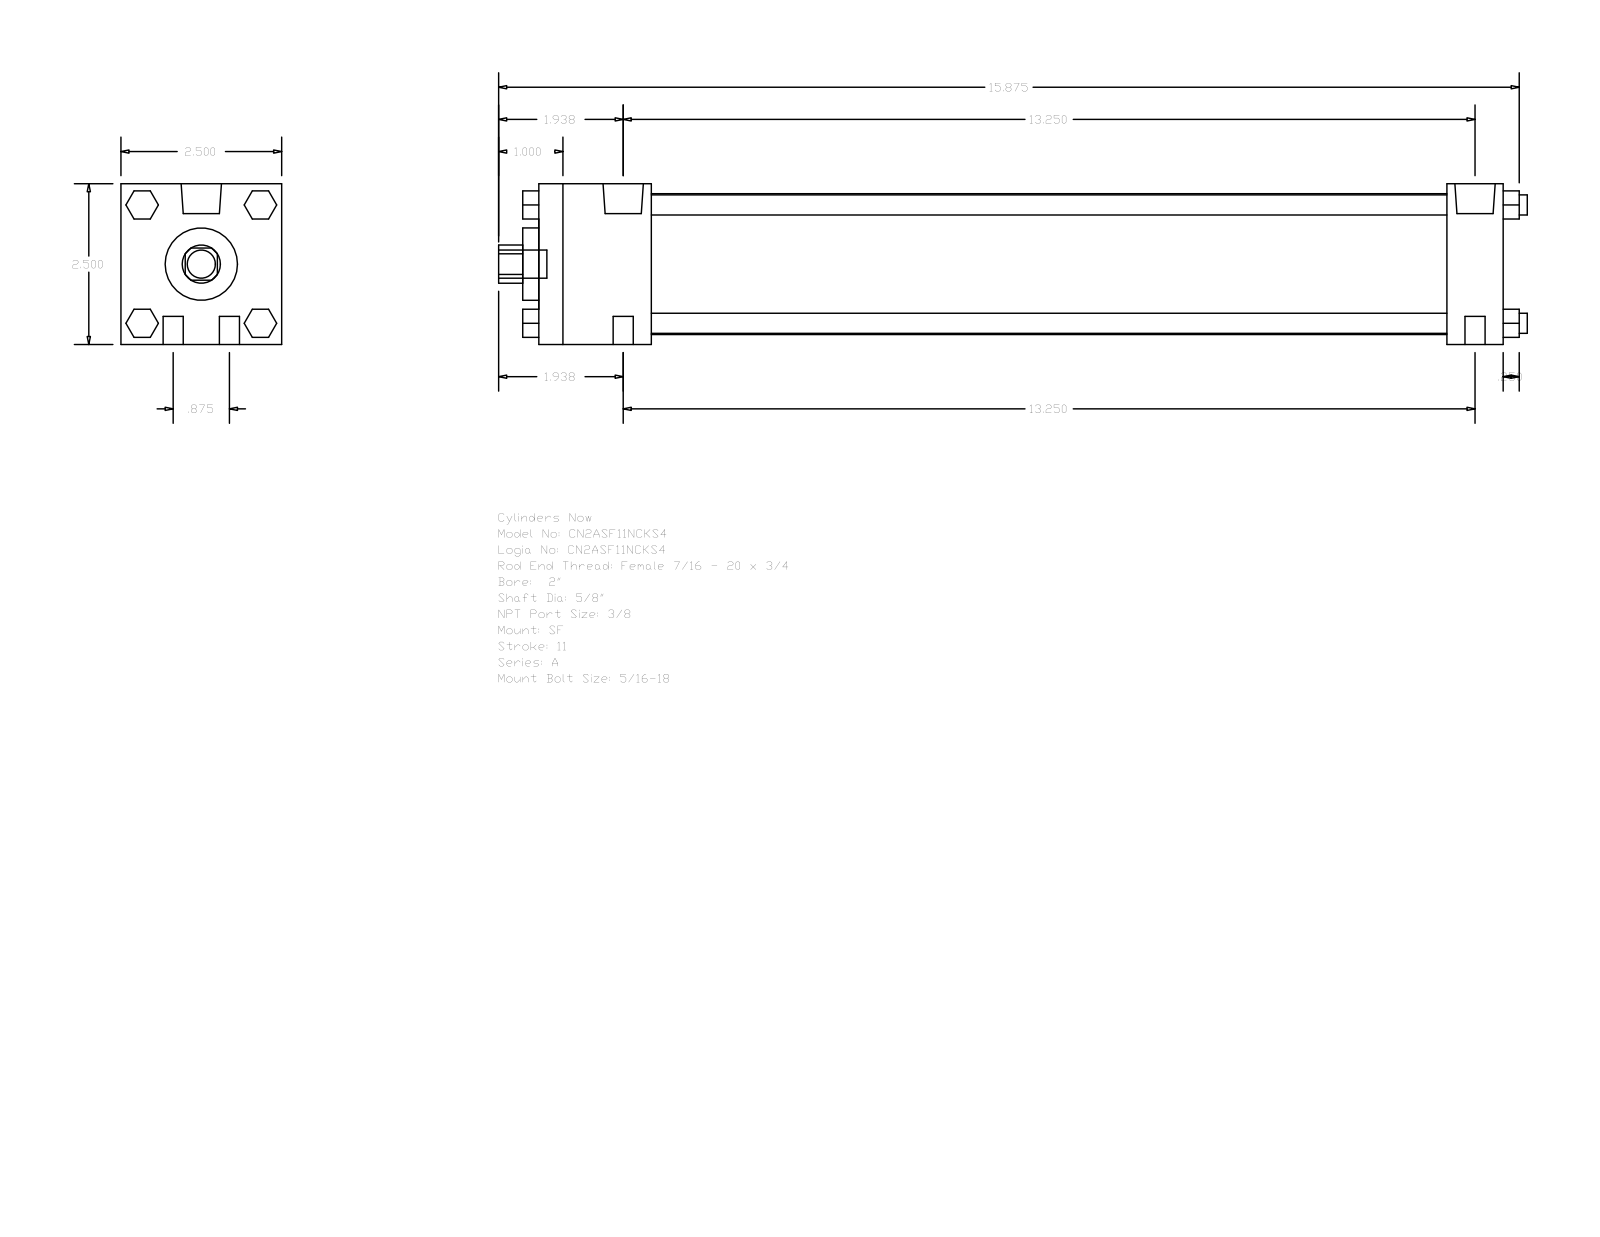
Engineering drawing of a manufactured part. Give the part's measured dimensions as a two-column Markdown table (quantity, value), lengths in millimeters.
| quantity | value |
| --- | --- |
| part name | A_SF__0200_0.625 |
| STEP written by | GSSL Pune (CONFIG_CONTROL_DESIGN) |
| units | millimeters |
| bodies | 0 solids, 124 faces (94 planar, 30 cylindrical, 0 other) |
| overall size | 406.4 × 63.5 × 63.5 |
| round holes (diameter × count) | 15.88 × 1, 28.57 × 1, 55.63 × 1 |
| round bosses / shafts (diameter × count) | 7.94 × 8, 15.93 × 2, 5.56 × 2, 11.11 × 1 |
| partial cylindrical surfaces (radius × count) | 7.54 × 1 |
| main face-to-face distances | 63.5, 381, 358.77, 22.23, 44.45, 314.32, 336.55, 387.35, 6.35, 50.8 |
